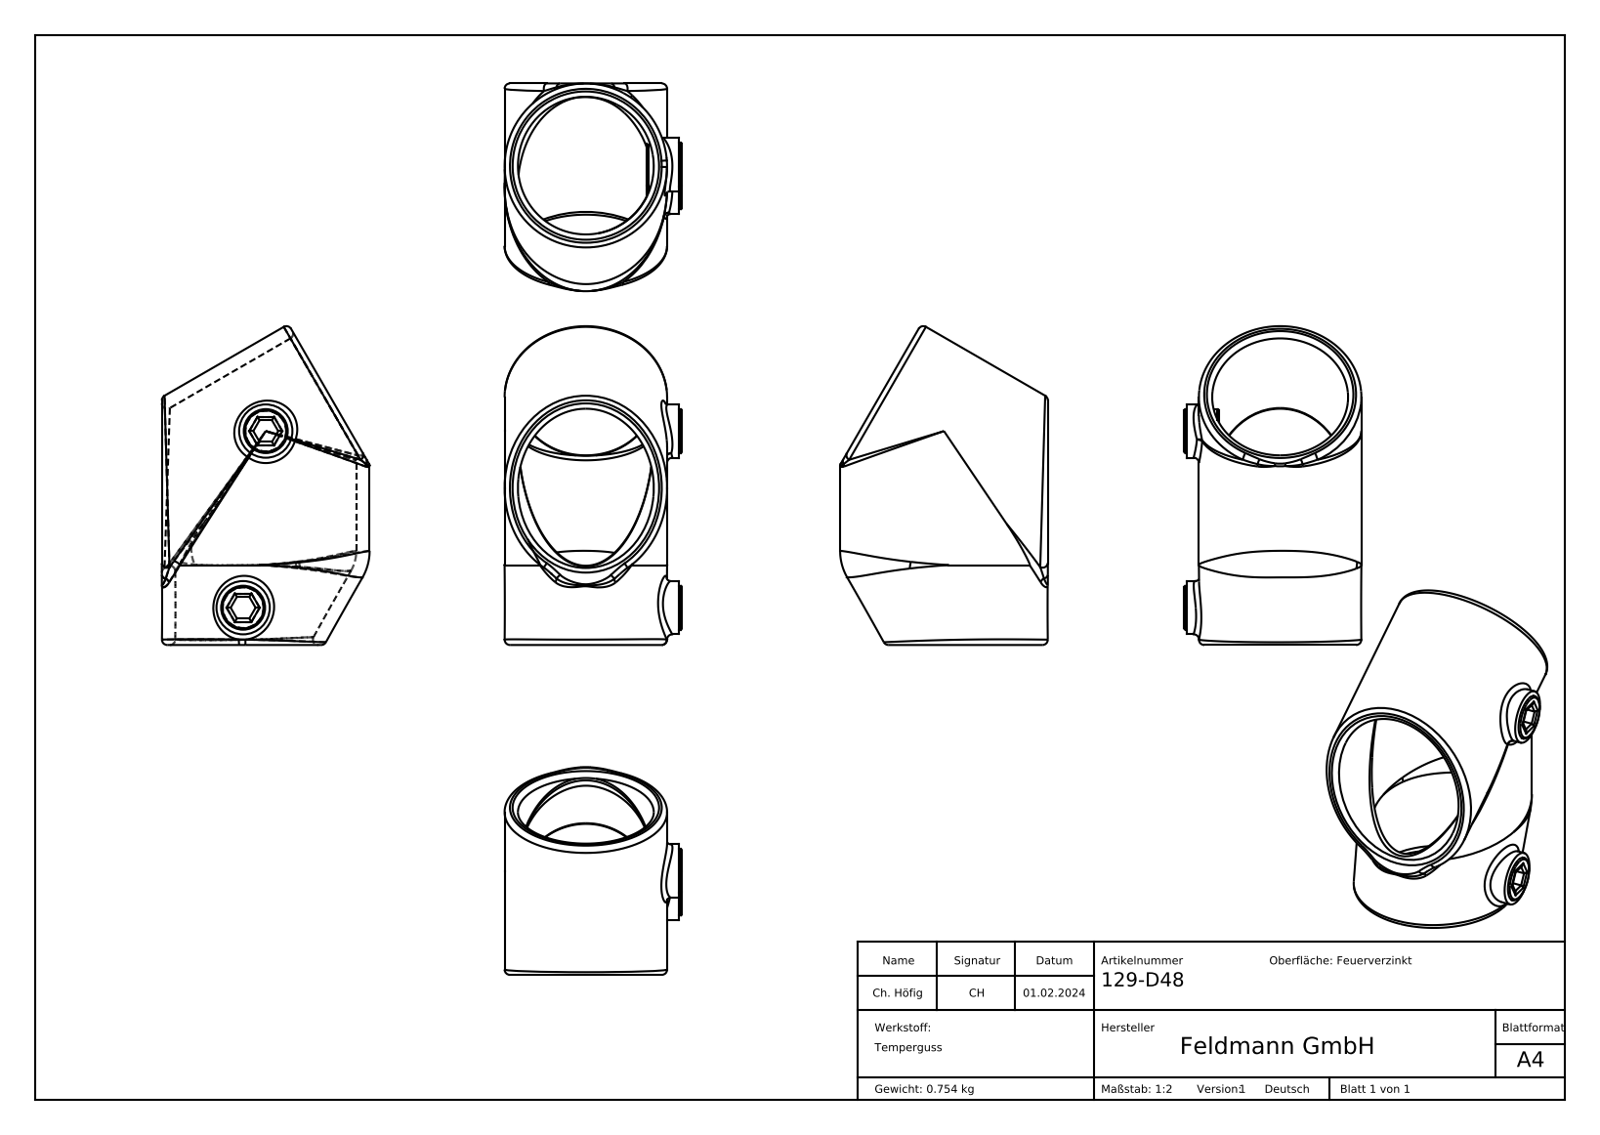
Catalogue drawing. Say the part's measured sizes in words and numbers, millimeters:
The part is named "129-D48 Teil1_129-D48 Teil1; 129-D48 Teil2_129-D48 Teil2; 129-D48". Its 3-D file was written by "SolidWorks 2018 (CONFIG_CONTROL_DESIGN)". It is 3 solids with 95 faces: 21 planar, 32 cylindrical and 42 other. Overall it measures 119.69 by 78 by 66.5 millimeters. Its volume is 103 288 cubic millimeters and its surface area 45 149 square millimeters. Round holes: 2 of diameter 15.25, 1 of diameter 51. Round bosses or shafts: 2 of diameter 20, 2 of diameter 16.5, 1 of diameter 61. Partial cylindrical surfaces (rounded edges, fillets, slot ends): 24 of radius 2. The main face-to-face distances are 8.1, 12, 13, 1, 66.3, 40.51, 18.05, 84.35, 63.89, 23.38. The hole center spacings are 66.84.
